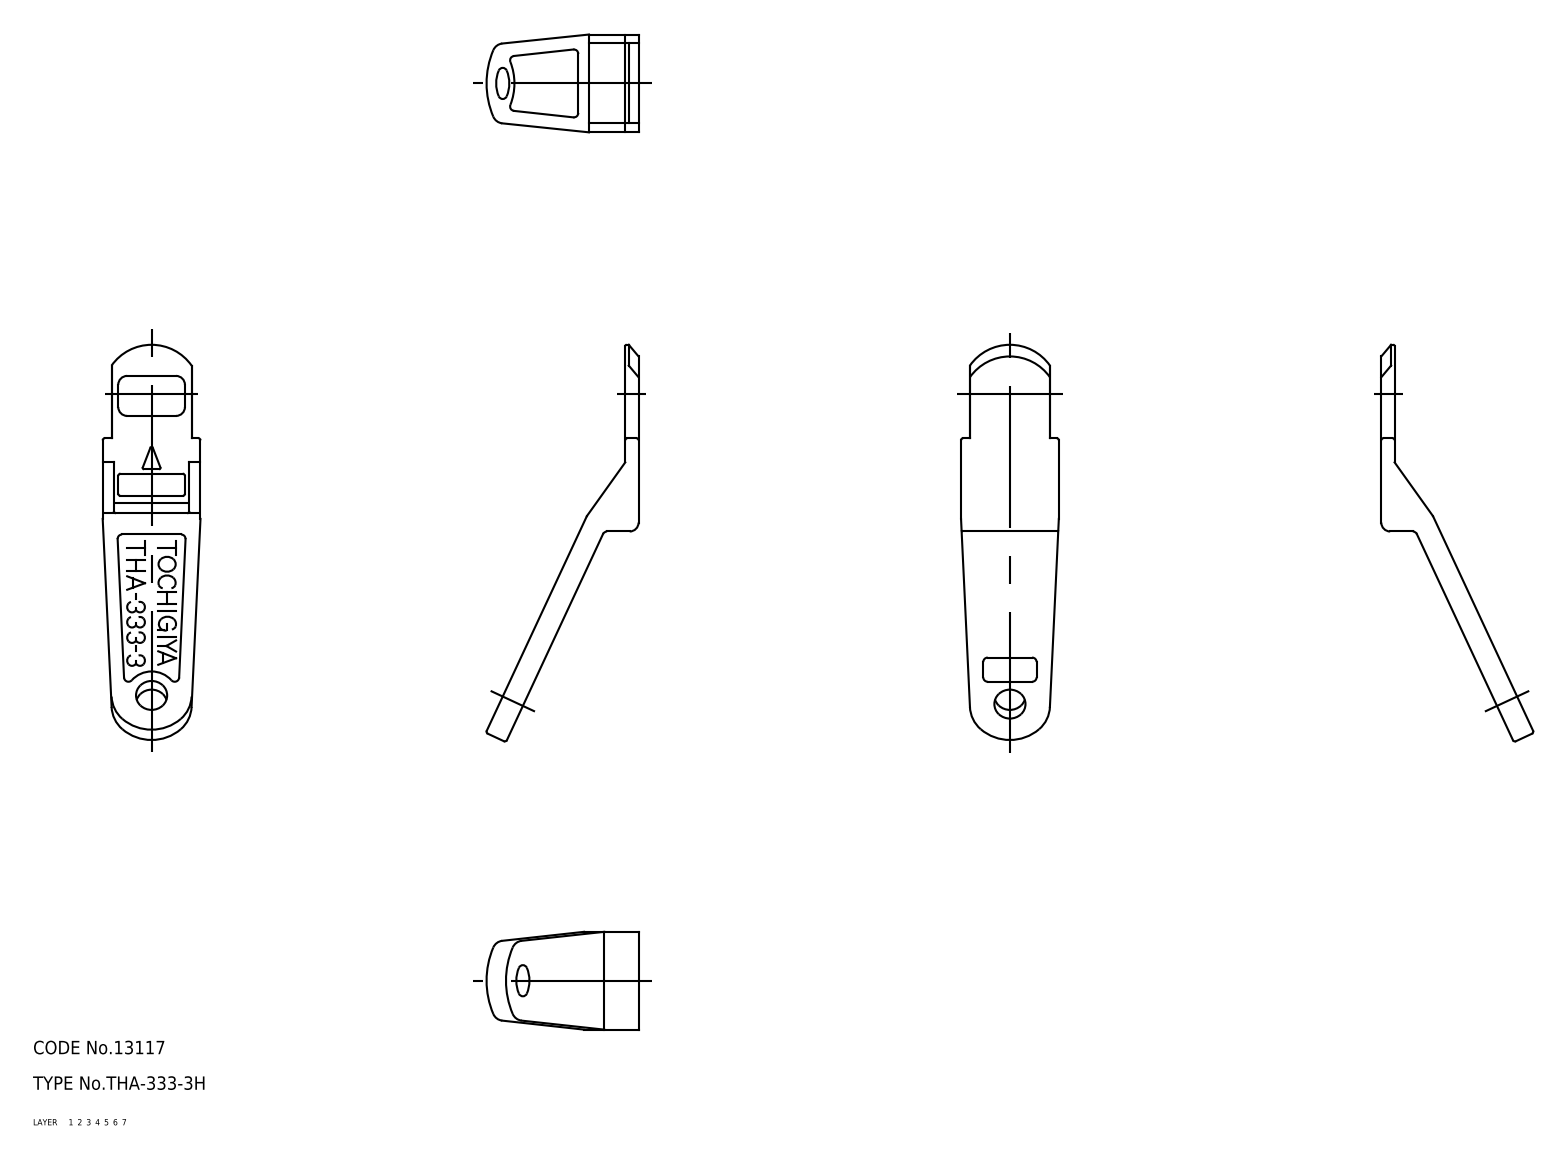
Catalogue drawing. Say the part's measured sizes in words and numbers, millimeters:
The part is named "key_handle". Its 3-D file was written by "CADfix (AUTOMOTIVE_DESIGN)". It is 1 solid with 87 faces: 0 planar, 0 cylindrical and 87 other. Overall it measures 89.24 by 34.2 by 22 millimeters. Its volume is 7 807 cubic millimeters and its surface area 5 009 square millimeters.
